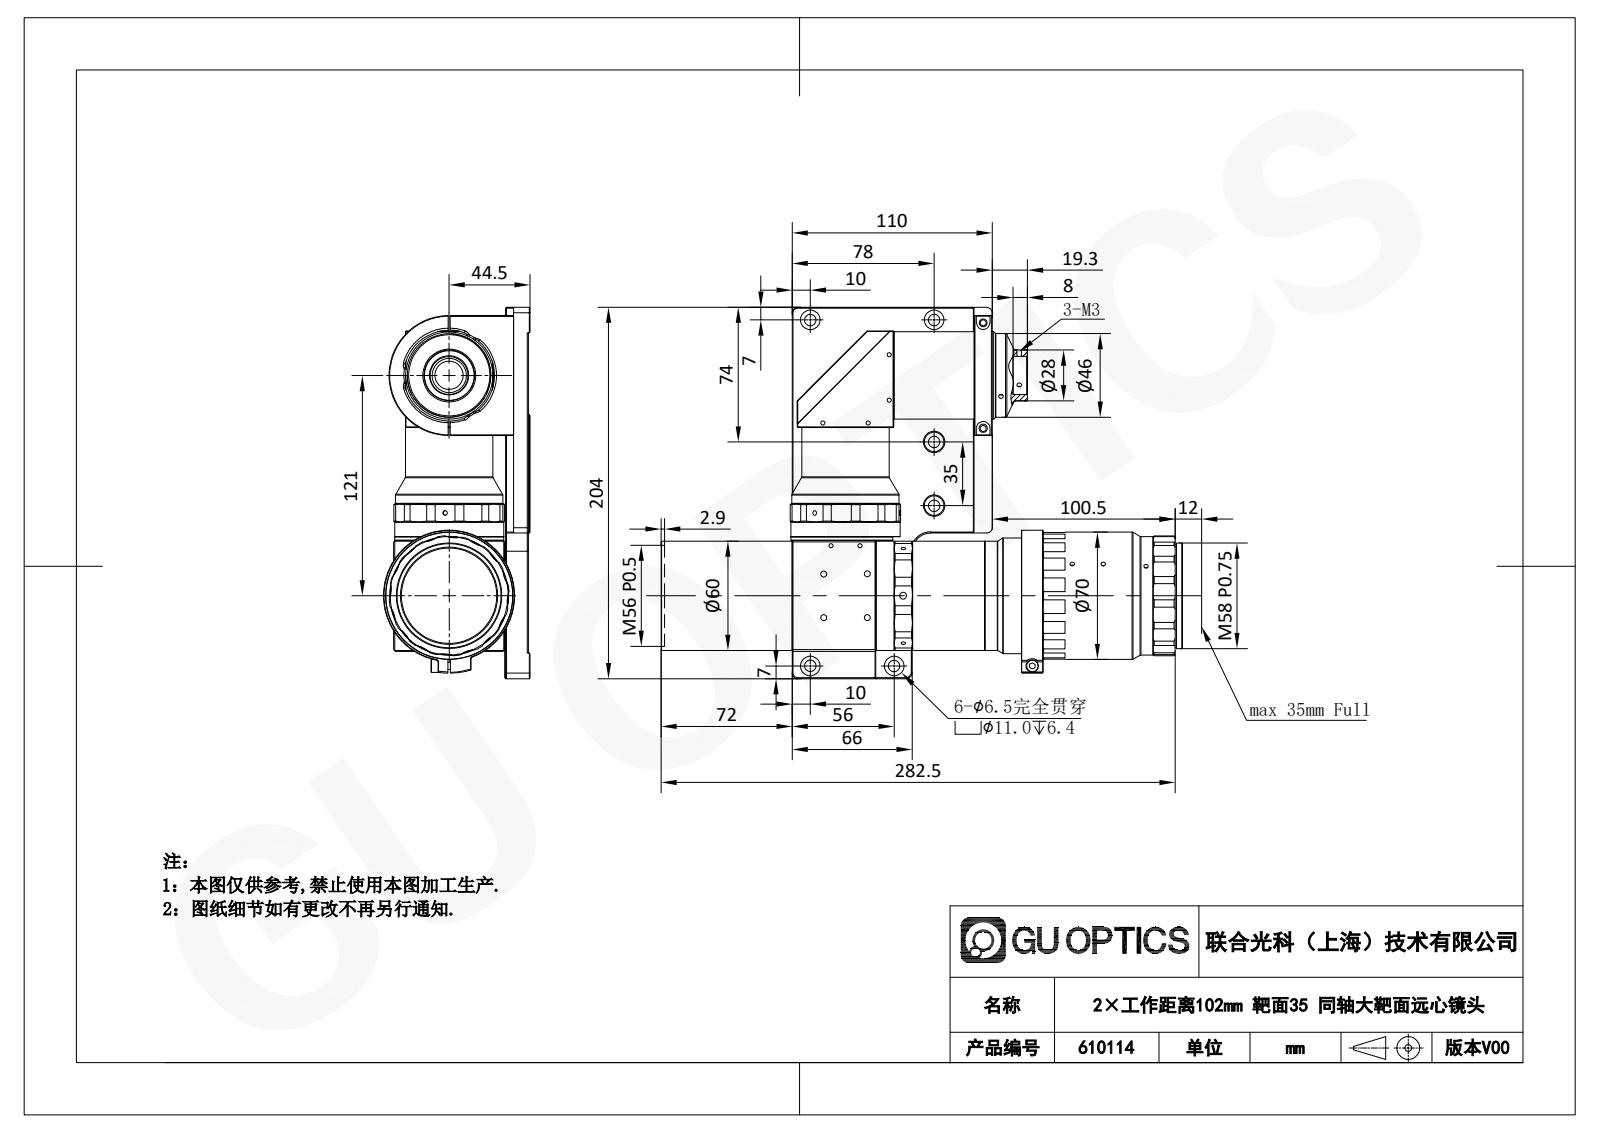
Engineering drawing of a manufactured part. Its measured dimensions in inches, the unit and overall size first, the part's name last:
Units: inches
Overall size (bounding box): 11.28 × 8.031 × 3.169
Round holes (diameter × count): ⌀0.098 ×22, ⌀0.13 ×15, ⌀0.094 ×13, ⌀0.177 ×12, ⌀0.295 ×9, ⌀0.256 ×6, ⌀0.433 ×6, ⌀0.126 ×4, ⌀0.236 ×4, ⌀0.059 ×2, ⌀0.087 ×2, ⌀0.134 ×1
Round bosses / shafts (diameter × count): ⌀2.362 ×2, ⌀1.89 ×2, ⌀2.835 ×1, ⌀2.756 ×1, ⌀2.677 ×1, ⌀2.638 ×1, ⌀2.559 ×1, ⌀2.5 ×1
Partial cylindrical surfaces — rounded edges, fillets, slot ends (radius × count): R0.591 ×34, R0.118 ×11, R0.079 ×10, R0.039 ×2, R0.148 ×2, R1.201 ×2, R0.157 ×1, R0.394 ×1
Main face-to-face distances: 0.492, 0.039, 0.531, 4.331, 2.421, 2.953, 2.913, 2.697, 2.657, 2.165
Hole centre spacings: 0.945, 1.575, 1.63, 0.028, 0.197, 0.668, 1.336, 1.63
Volume: 90.86 in³ · Surface area: 263.3 in²
Bodies: 1 solid, 1221 faces (370 planar, 446 cylindrical, 405 other)
Part name (STEP PRODUCT): DTCA35F-22C-G-M58-AL
STEP written by: SolidWorks 2017 (CONFIG_CONTROL_DESIGN)
